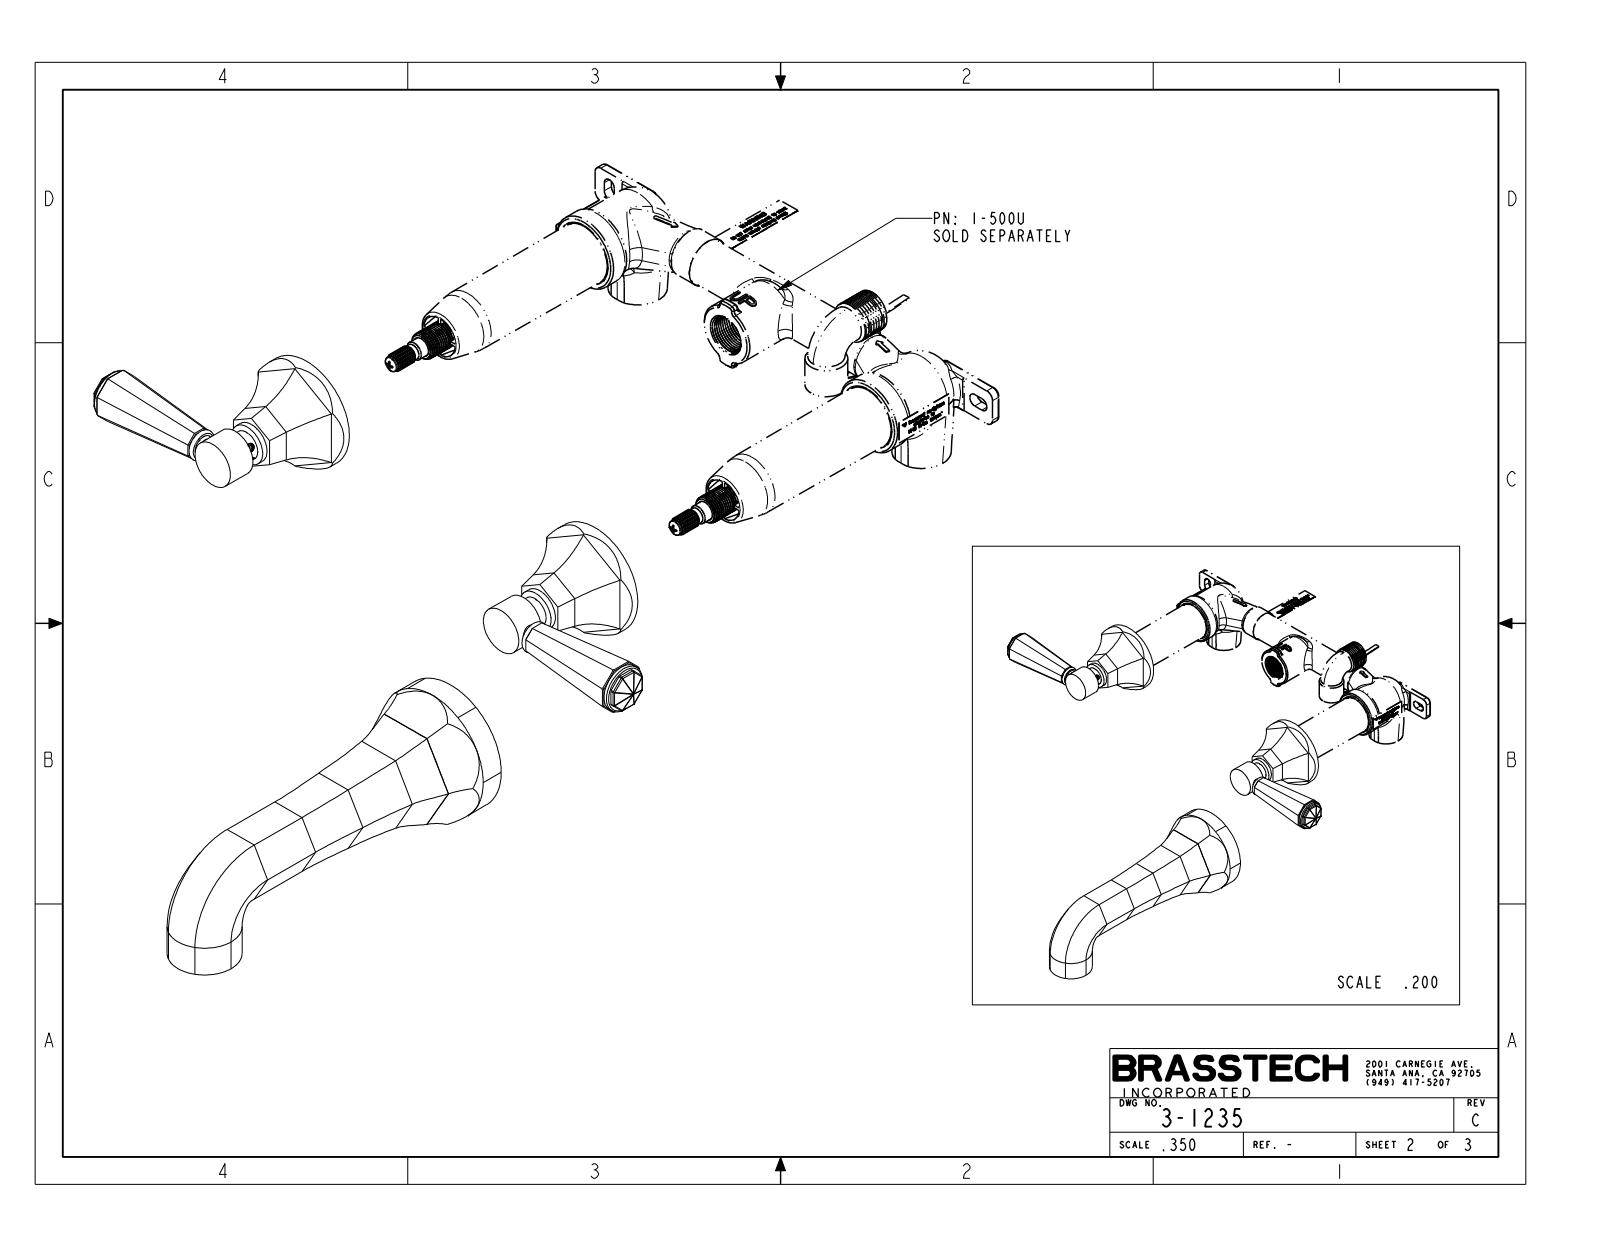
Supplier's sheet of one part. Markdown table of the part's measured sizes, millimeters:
| quantity | value |
| --- | --- |
| part name | 3-1235_SW0001 |
| STEP written by | CREO PARAMETRIC BY PTC INC, 2018400 (AUTOMOTIVE_DESIGN) |
| units | millimeters |
| bodies | 3 solids, 398 faces (178 planar, 134 cylindrical, 86 other) |
| overall size | 373.8 × 224.4 × 192.1 |
| volume | 440 200 mm³ |
| surface area | 83 100 mm² |
| round holes (diameter × count) | 9.8 × 1 |
| round bosses / shafts (diameter × count) | 24.9 × 3, 60.3 × 2, 21.8 × 2, 17.8 × 2, 15.9 × 2, 71.1 × 1, 9.3 × 1 |
| partial cylindrical surfaces (radius × count) | 0.8 × 40, 39.1 × 12, 41.7 × 12, 54 × 6, 27.4 × 2 |
| main face-to-face distances | 4.8, 2.5, 4.3, 4.3, 33, 99.8, 25.3, 58.3, 50.2, 45.4 |
